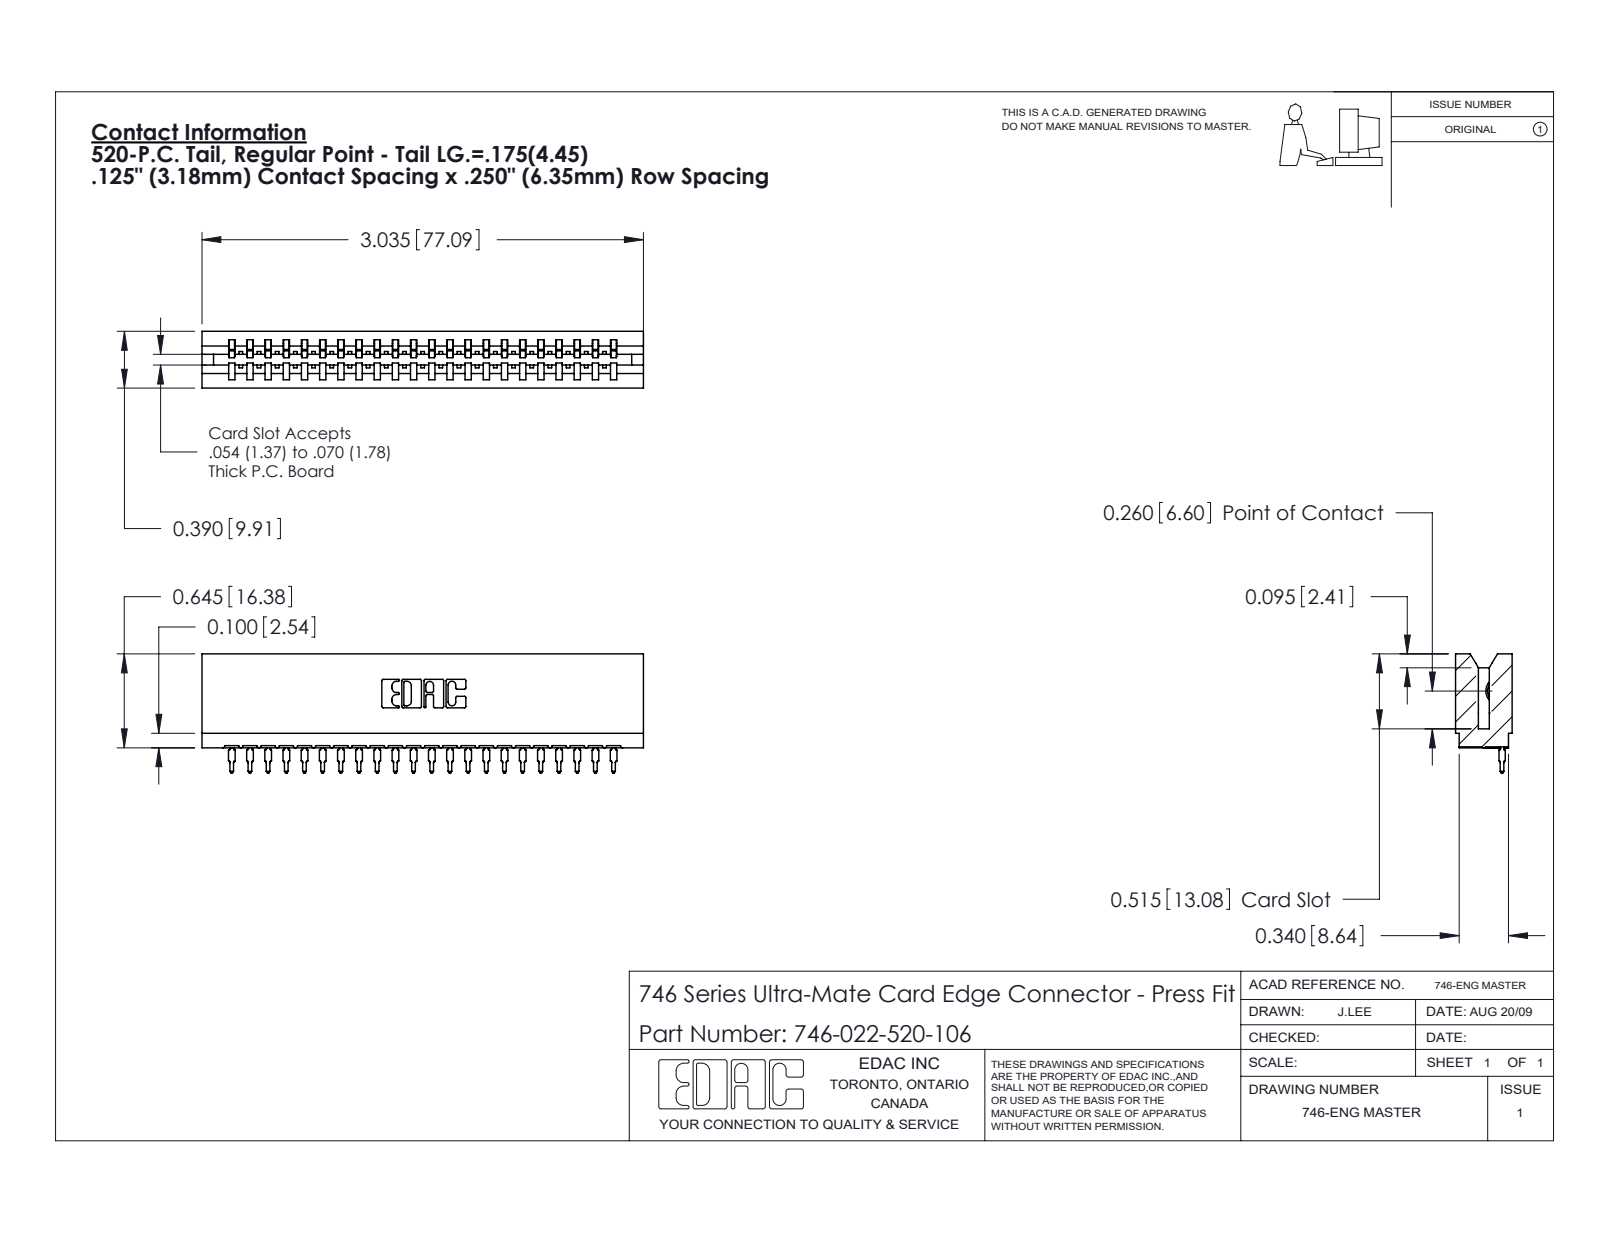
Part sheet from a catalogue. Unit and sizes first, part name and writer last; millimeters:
Units: millimetres
Overall size (bounding box): 77.1 × 20.8 × 9.9
Partial cylindrical surfaces — rounded edges, fillets, slot ends (radius × count): R0.5 ×44, R0.4 ×23, R0.3 ×22, R0.2 ×6, R0.8 ×6, R0.1 ×4, R0.3 ×4, R0.7 ×3
Main face-to-face distances: 8.5, 1.4, 6.4, 9.9, 12.7, 1.1, 0.6, 7.8, 2.1, 3.2
Volume: 8 130 mm³ · Surface area: 11 590 mm²
Bodies: 23 solids, 2474 faces (1442 planar, 460 cylindrical, 572 other)
Part name (STEP PRODUCT): 746 Part_.515 Slot Depth - 06; 746-292-001_520; 746-022-520-106
STEP written by: SolidWorks 2020 (CONFIG_CONTROL_DESIGN)
